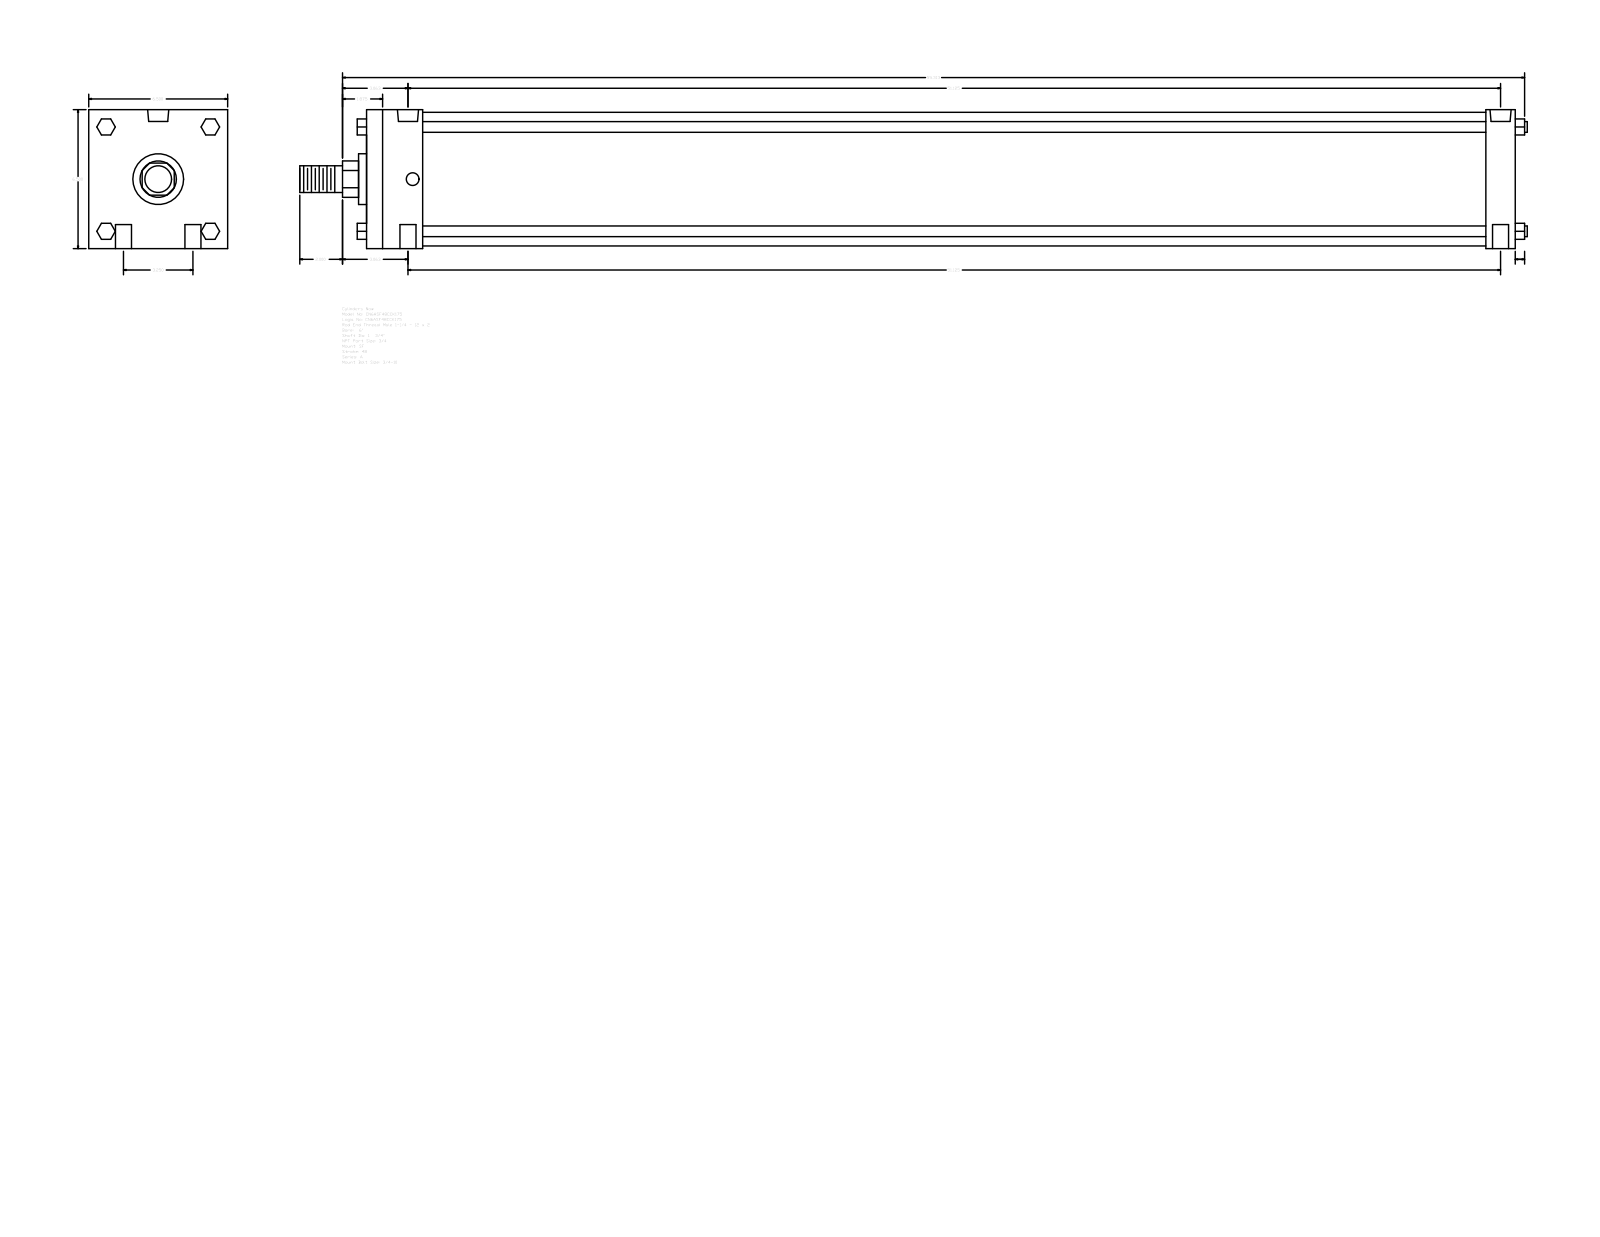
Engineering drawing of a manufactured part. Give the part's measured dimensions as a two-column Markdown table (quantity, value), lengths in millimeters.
| quantity | value |
| --- | --- |
| part name | A_SF__0600_1.75 |
| STEP written by | GSSL Pune (CONFIG_CONTROL_DESIGN) |
| units | millimeters |
| bodies | 0 solids, 124 faces (94 planar, 30 cylindrical, 0 other) |
| overall size | 1458.91 × 165.1 × 165.1 |
| round holes (diameter × count) | 19.05 × 4, 15.08 × 2, 25.12 × 2 |
| round bosses / shafts (diameter × count) | 12.7 × 4, 158.75 × 1, 60.33 × 1, 44.45 × 1, 31.75 × 1 |
| partial cylindrical surfaces (radius × count) | 21.63 × 1 |
| main face-to-face distances | 165.1, 1365.26, 66.68, 1330.33, 34.93, 1263.65, 1298.58, 19.05, 61.97, 107.34 |
| hole center spacings | 41.27, 1299.23, 1298.57, 82.54, 1301.19, 1287.45 |
